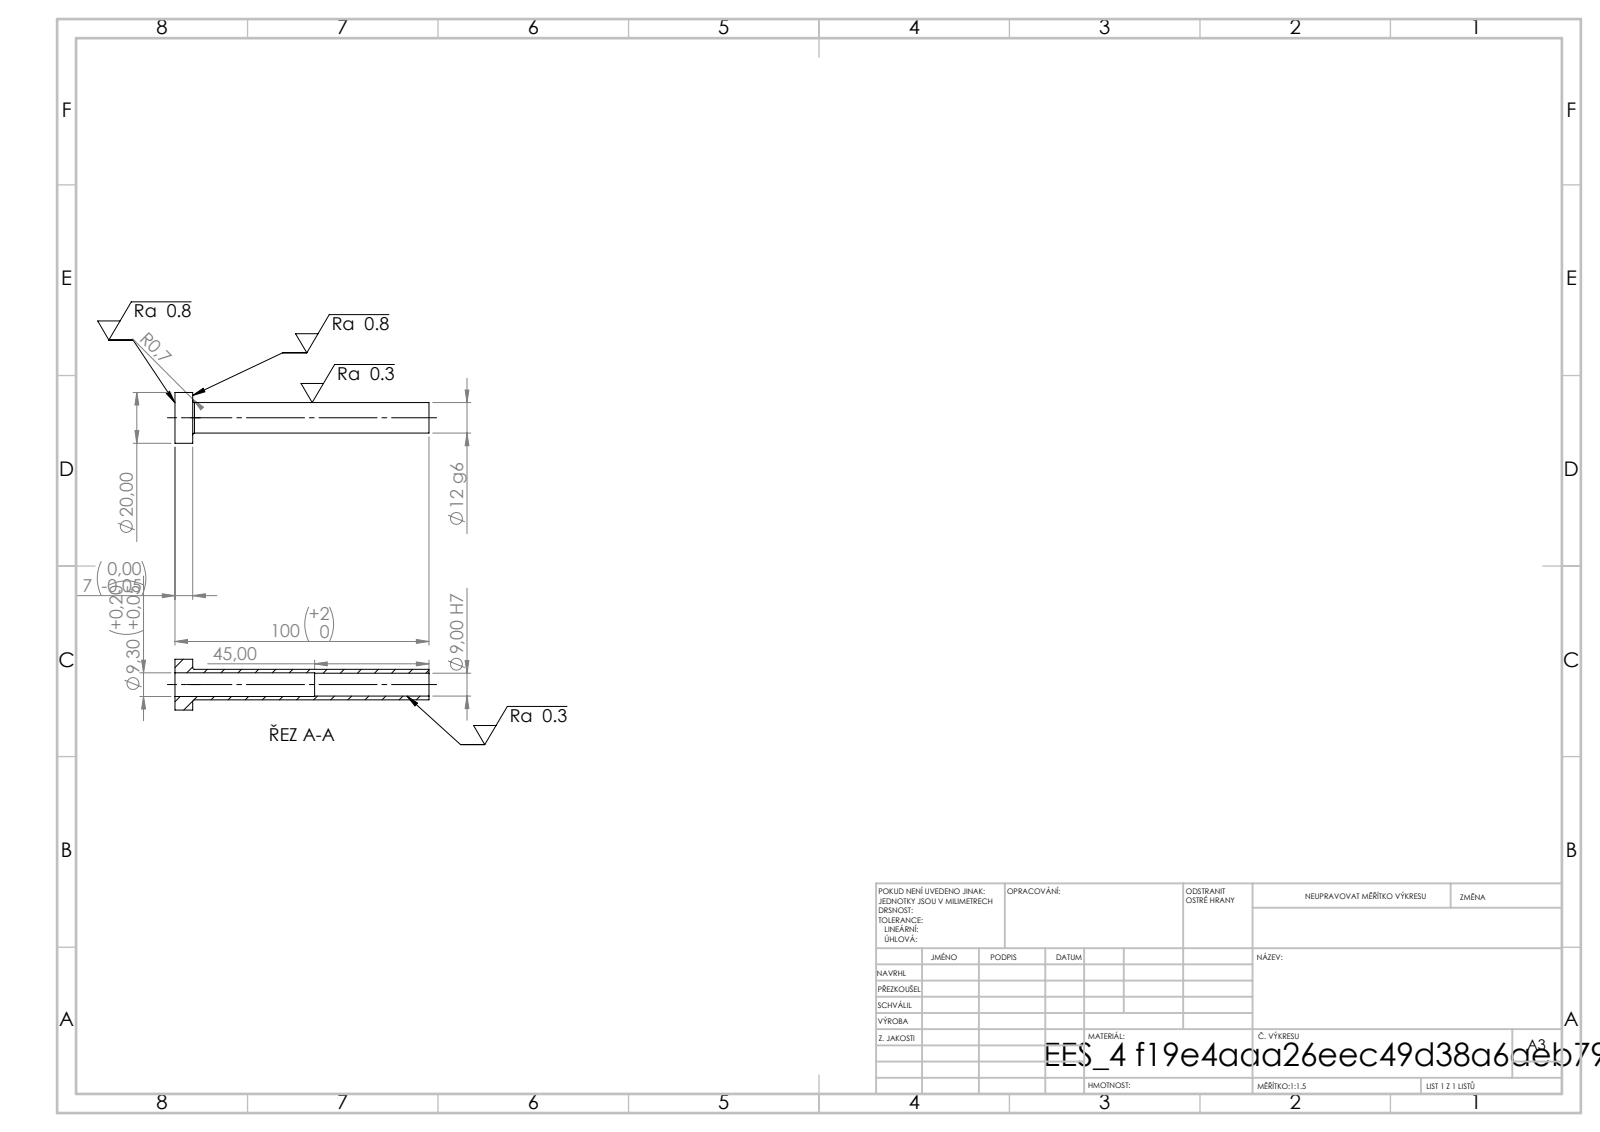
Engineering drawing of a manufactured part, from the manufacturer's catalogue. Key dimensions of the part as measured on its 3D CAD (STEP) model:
STEP written by: SolidWorks 2019 (CONFIG_CONTROL_DESIGN)
Units: millimetres
Bodies: 1 solid, 14 faces (4 planar, 8 cylindrical, 2 other)
Overall size (bounding box): 100 × 20 × 20
Volume: 6 122 mm³ · Surface area: 7 315 mm²
Round holes (diameter × count): ⌀9 ×1, ⌀9.3 ×1
Round bosses / shafts (diameter × count): ⌀20 ×1, ⌀12 ×1
Main face-to-face distances: 7, 100, 93, 55, 48, 45
